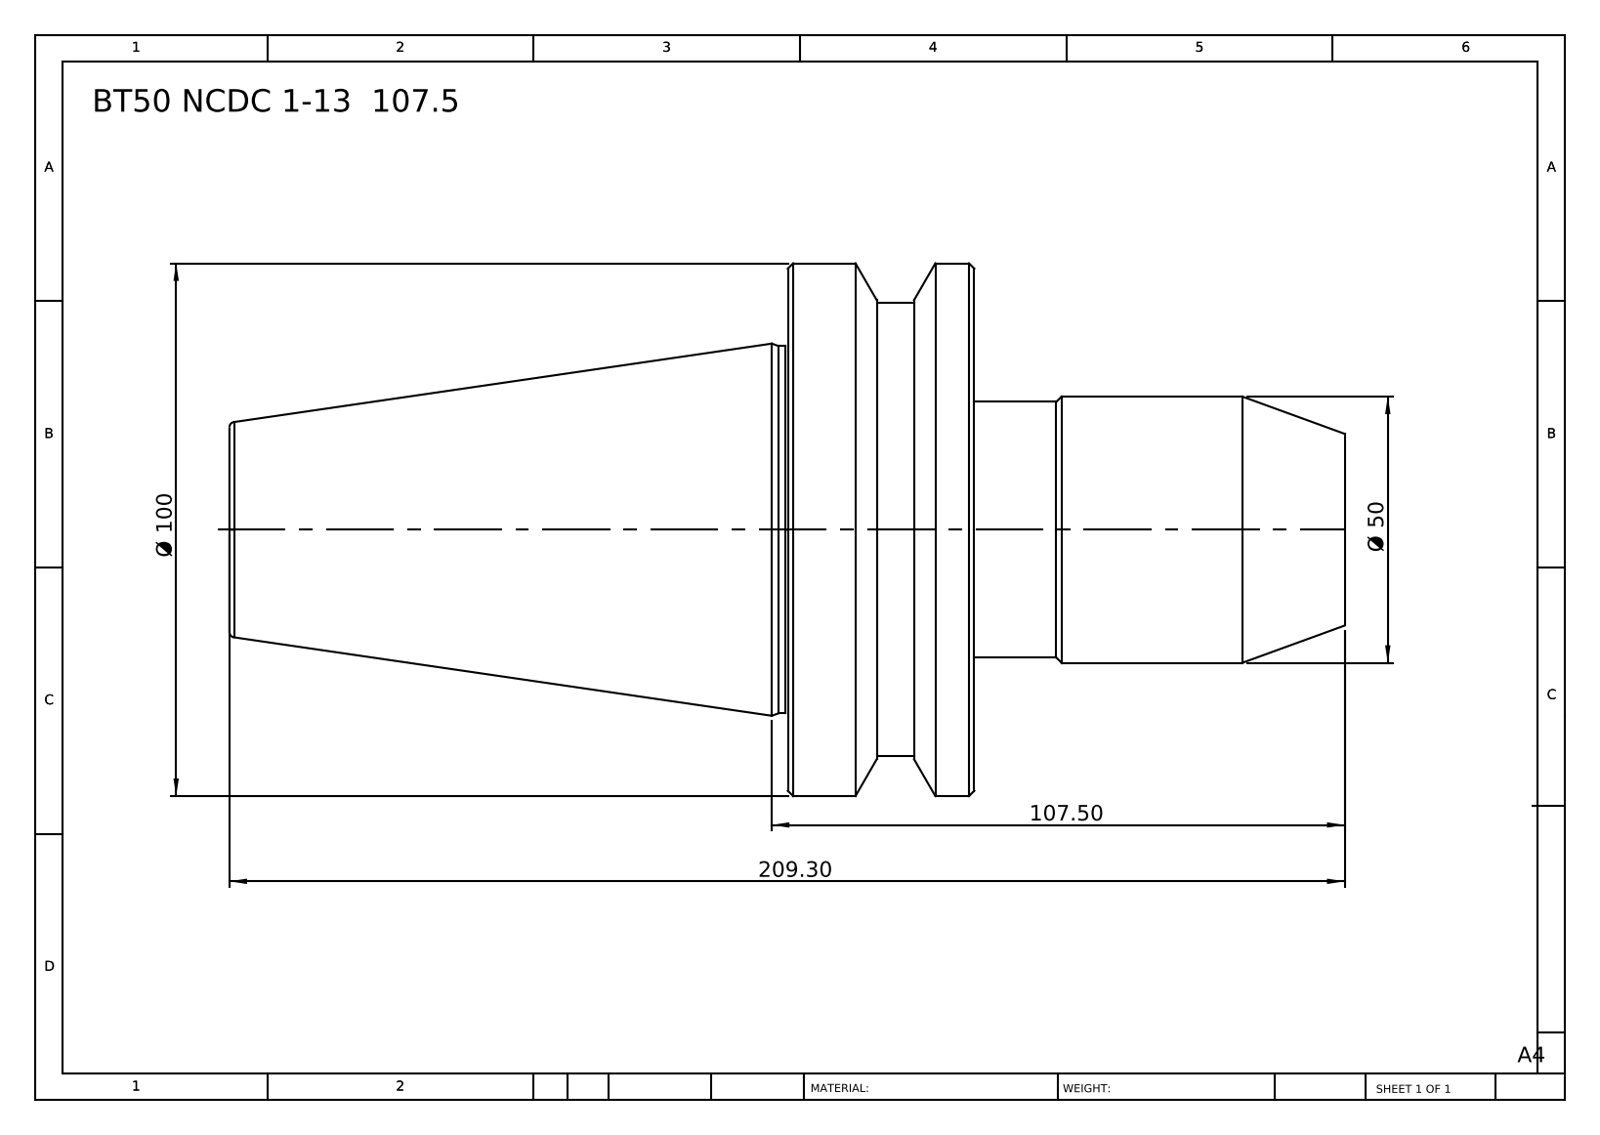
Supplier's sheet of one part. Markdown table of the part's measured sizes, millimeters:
| quantity | value |
| --- | --- |
| part name | BT50 NCDC 1-13 107.5 |
| STEP written by | SolidWorks 2014 (CONFIG_CONTROL_DESIGN) |
| units | millimeters |
| bodies | 1 solid, 38 faces (6 planar, 12 cylindrical, 20 other) |
| overall size | 209.3 × 100 × 100 |
| volume | 634 499 mm³ |
| surface area | 54 197 mm² |
| round bosses / shafts (diameter × count) | 100 × 1, 85 × 1, 69 × 1, 50 × 1, 48 × 1 |
| main face-to-face distances | 35, 139.8, 104.8, 69.5, 104.5, 209.3, 80.8, 11.3, 23.7, 128.5 |
